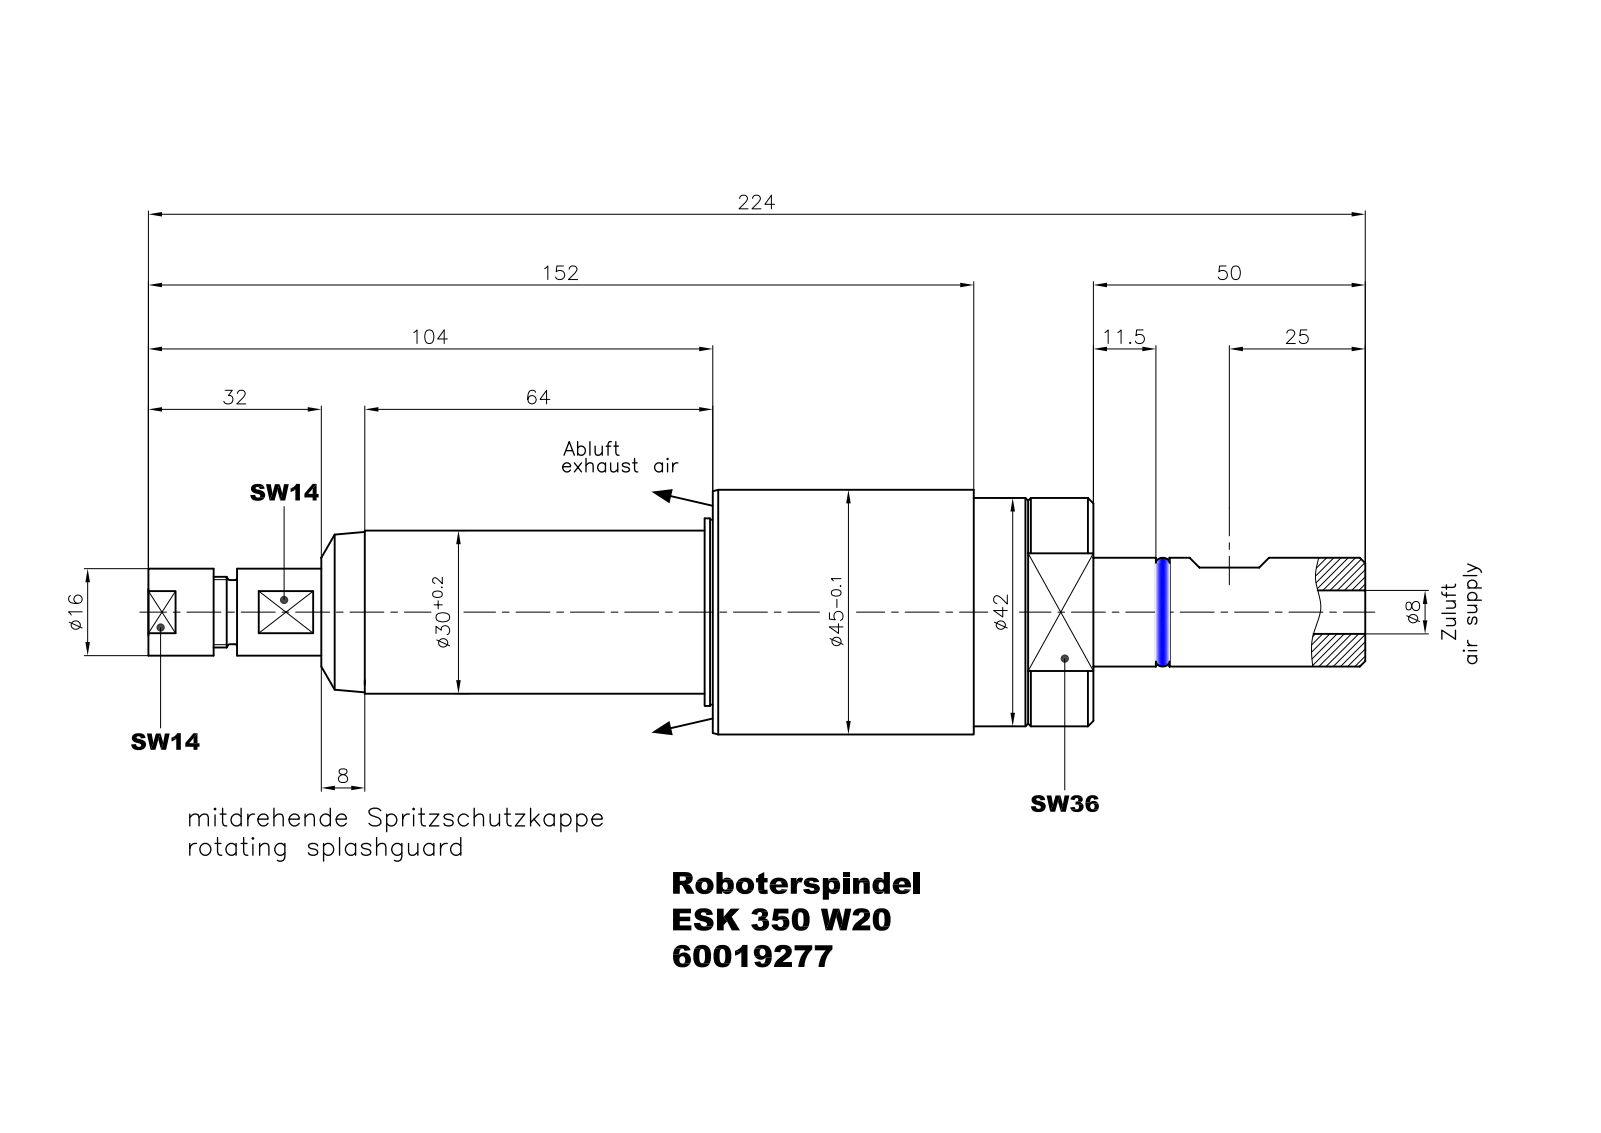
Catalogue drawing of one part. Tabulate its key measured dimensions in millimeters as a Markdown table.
| quantity | value |
| --- | --- |
| part name | ESK 350 W20_60019277 |
| STEP written by | Autodesk Inventor 2012 (AUTOMOTIVE_DESIGN) |
| units | millimeters |
| bodies | 1 solid, 149 faces (71 planar, 40 cylindrical, 38 other) |
| overall size | 224.24 × 45 × 45 |
| volume | 172 827 mm³ |
| surface area | 27 720 mm² |
| round holes (diameter × count) | 1 × 1, 3 × 1, 8 × 1, 9 × 1, 9.19 × 1 |
| round bosses / shafts (diameter × count) | 45 × 1, 42 × 1, 34.5 × 1, 34 × 1, 30 × 1, 20 × 1, 16.25 × 1, 16 × 1 |
| partial cylindrical surfaces (radius × count) | 19 × 4, 22.5 × 4, 4.12 × 1 |
| main face-to-face distances | 69, 36, 2.5, 72, 0.7, 120, 71.5, 11, 25, 14 |
